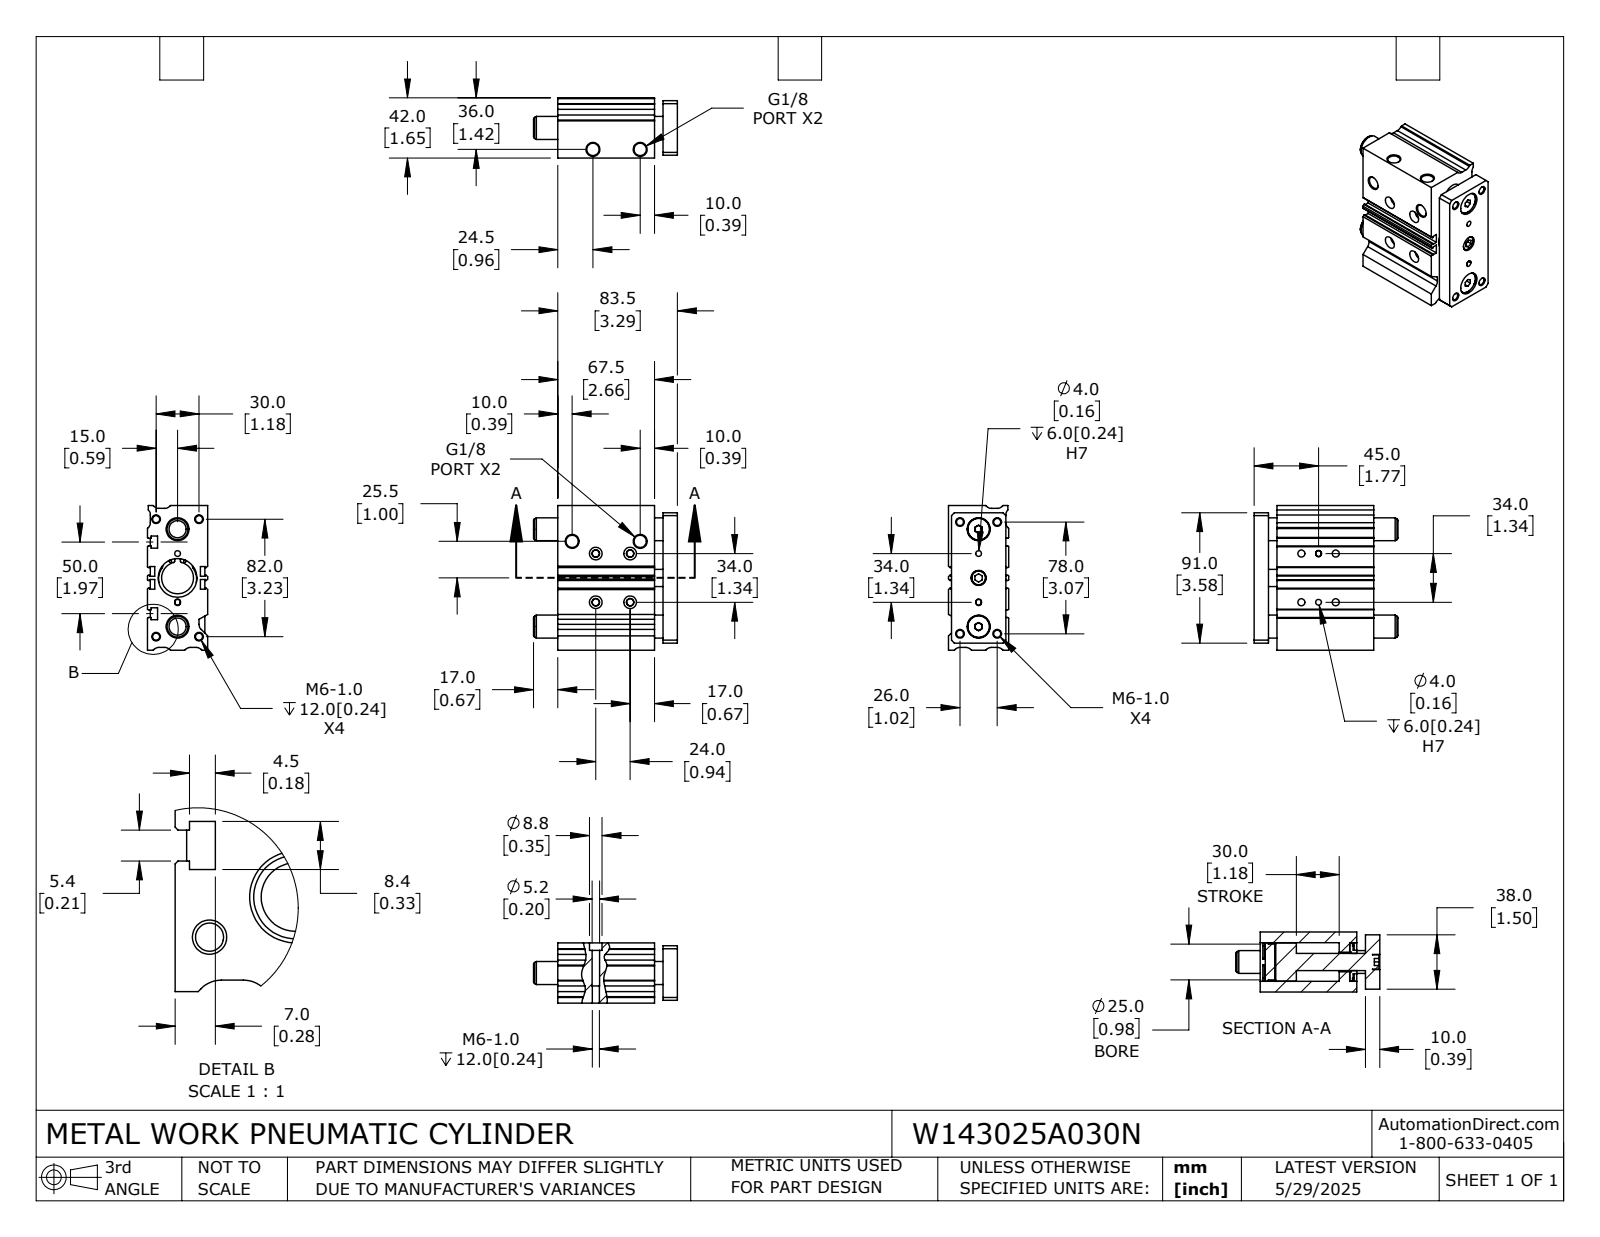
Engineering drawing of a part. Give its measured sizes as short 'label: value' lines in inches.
name: W143025A030N_BODY; W143025A030N; W143025A030N_ROD
written by: SolidWorks 2024 (CONFIG_CONTROL_DESIGN)
unit: in
bodies: 6 solids, 390 faces (191 planar, 157 cylindrical, 42 other)
size: 3.976 × 3.957 × 1.654
volume: 17.07 in³; area: 120.9 in²
holes: 8× ⌀0.194, 4× ⌀0.067, 4× ⌀0.157, 4× ⌀0.194, 4× ⌀0.205, 4× ⌀0.337, 4× ⌀0.346, 2× ⌀0.63, 1× ⌀0.413, 1× ⌀0.472, 1× ⌀0.539, 1× ⌀0.874
bosses: 2× ⌀0.61, 1× ⌀1.063, 1× ⌀0.984, 1× ⌀0.65, 1× ⌀0.394
rounds: 12× R0.039, 9× R0.197, 8× R0.079, 2× R0.524, 1× R0.559
face distances: 0.197, 0.079, 1.654, 0.236, 1.378, 0.63, 0.394, 0.118, 3.287, 2.894
hole spacings: 1.339, 0.111, 0.29, 0.472, 0.5, 0.548, 0.652, 0.669
